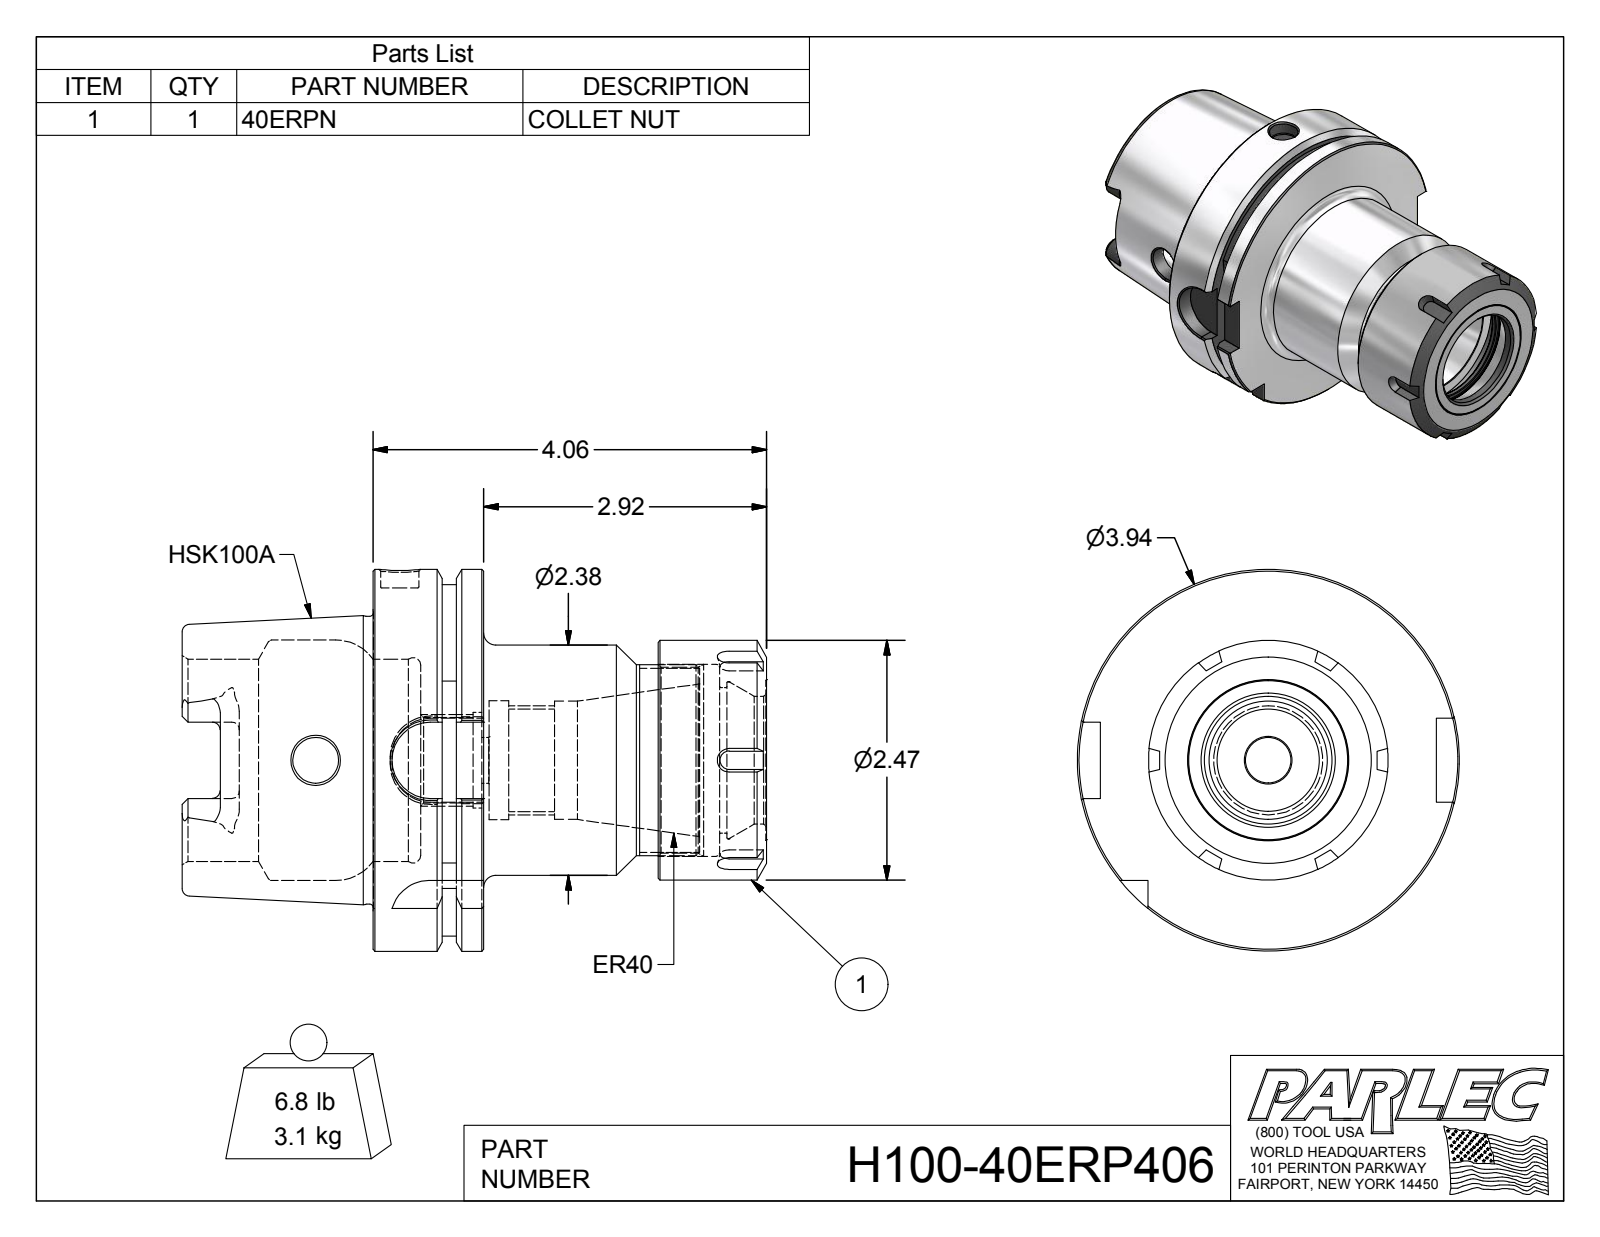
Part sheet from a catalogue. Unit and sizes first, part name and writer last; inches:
Units: inches
Overall size (bounding box): 6.029 × 3.937 × 3.937
Round holes (diameter × count): ⌀0.472 ×2, ⌀0.394 ×1, ⌀0.881 ×1, ⌀0.985 ×1, ⌀1.057 ×1, ⌀1.22 ×1, ⌀1.225 ×1, ⌀1.318 ×1, ⌀1.5 ×1, ⌀1.62 ×1, ⌀1.916 ×1, ⌀1.98 ×1
Round bosses / shafts (diameter × count): ⌀3.937 ×1, ⌀2.967 ×1, ⌀2.47 ×1, ⌀2.375 ×1, ⌀1.969 ×1
Partial cylindrical surfaces — rounded edges, fillets, slot ends (radius × count): R0.079 ×6, R0.192 ×4, R0.394 ×4, R1.811 ×1
Main face-to-face distances: 1.142, 0.492, 0.65, 4.06, 3.568, 2.918, 2.94, 2.448, 1.798, 1.12
Volume: 24.01 in³ · Surface area: 121.7 in²
Bodies: 2 solids, 179 faces (68 planar, 42 cylindrical, 69 other)
Part name (STEP PRODUCT): H100-40ERP406; H100-40ER4-1; 40ERPN
STEP written by: Autodesk Inventor 2012 (AUTOMOTIVE_DESIGN)
